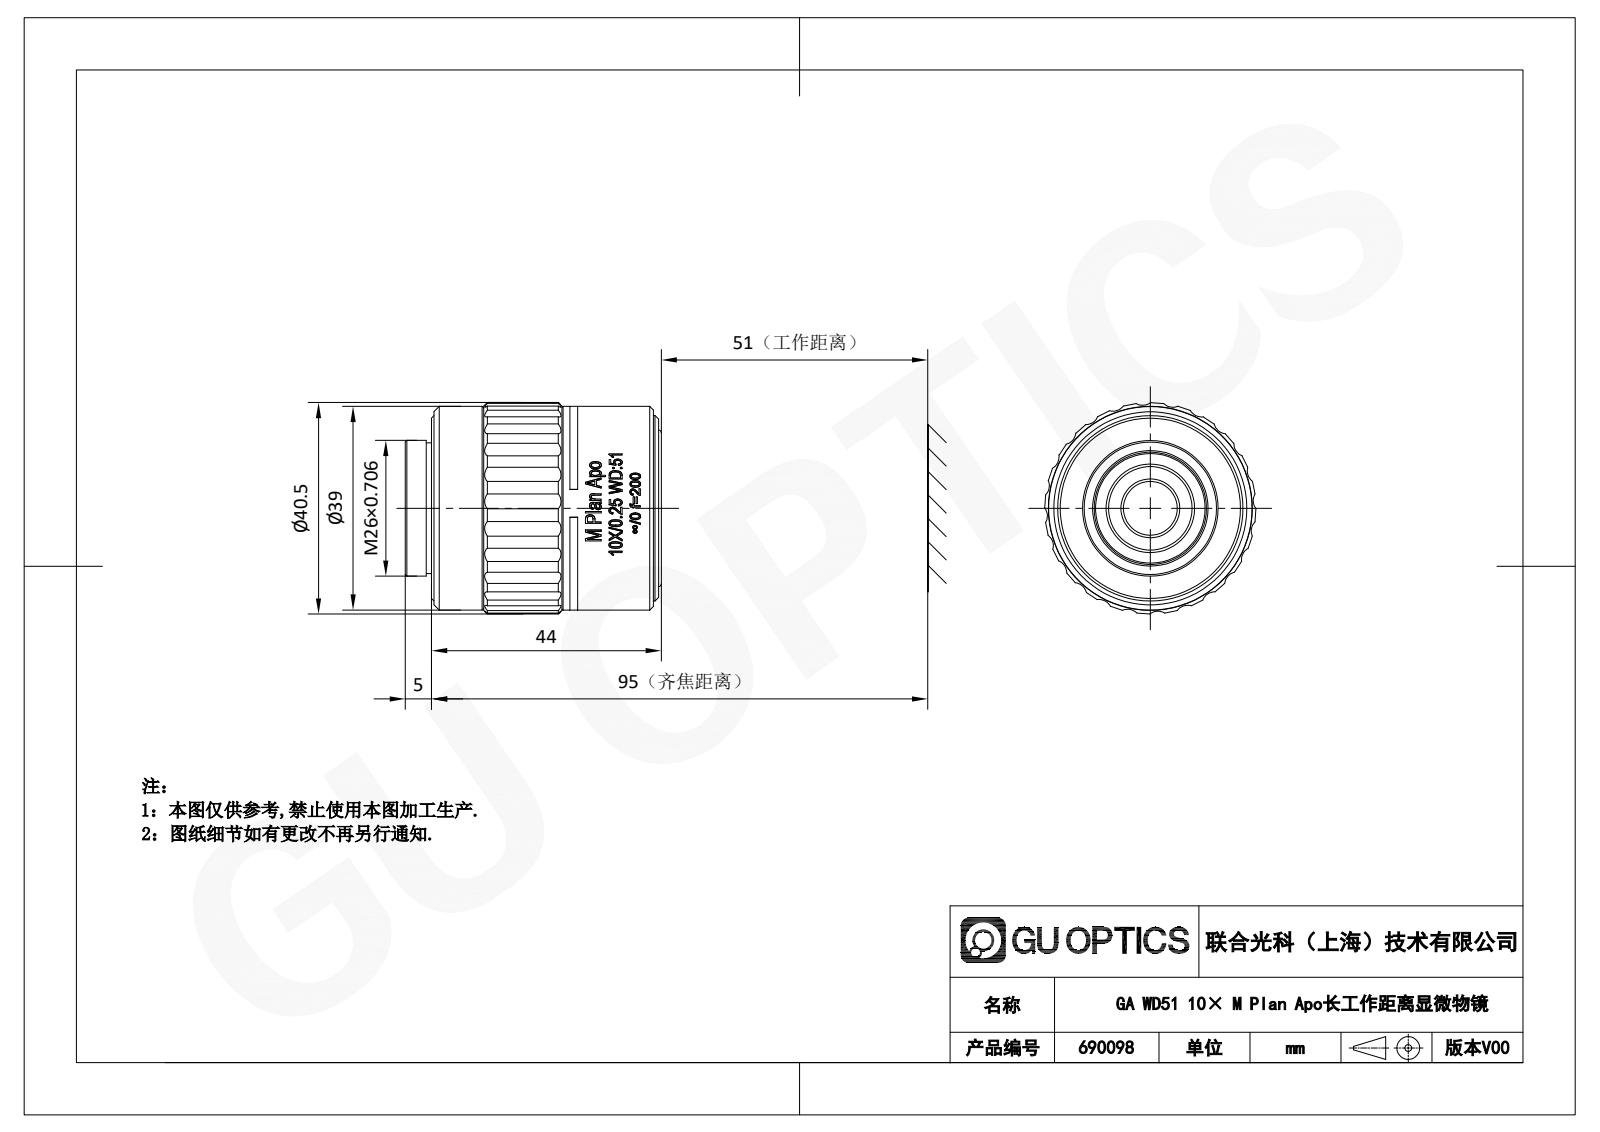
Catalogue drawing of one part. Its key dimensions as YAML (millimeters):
part_name: "690098"
step_written_by: "SolidWorks 2024 (CONFIG_CONTROL_DESIGN)"
units: millimeters
bodies: {solids: 0, faces: 326, planar: 50, cylindrical: 181, other: 95}
overall_size: [100.1, 40.5, 40.5]
round_holes:
  - {diameter: 10.34, count: 1}
  - {diameter: 21.5, count: 1}
  - {diameter: 30.2, count: 1}
round_bosses_or_shafts:
  - {diameter: 39.02, count: 1}
  - {diameter: 39, count: 1}
  - {diameter: 35.5, count: 1}
  - {diameter: 32, count: 1}
  - {diameter: 30, count: 1}
  - {diameter: 26, count: 1}
  - {diameter: 25, count: 1}
partial_cylinders:
  - {radius: 2.5, count: 24}
  - {radius: 13.25, count: 1}
  - {radius: 20.25, count: 1}
face_to_face_distances: [95.11, 95.01, 43.5, 0.5, 4.83, 48.33, 51.61, 51.51, 52.61, 52.51]
